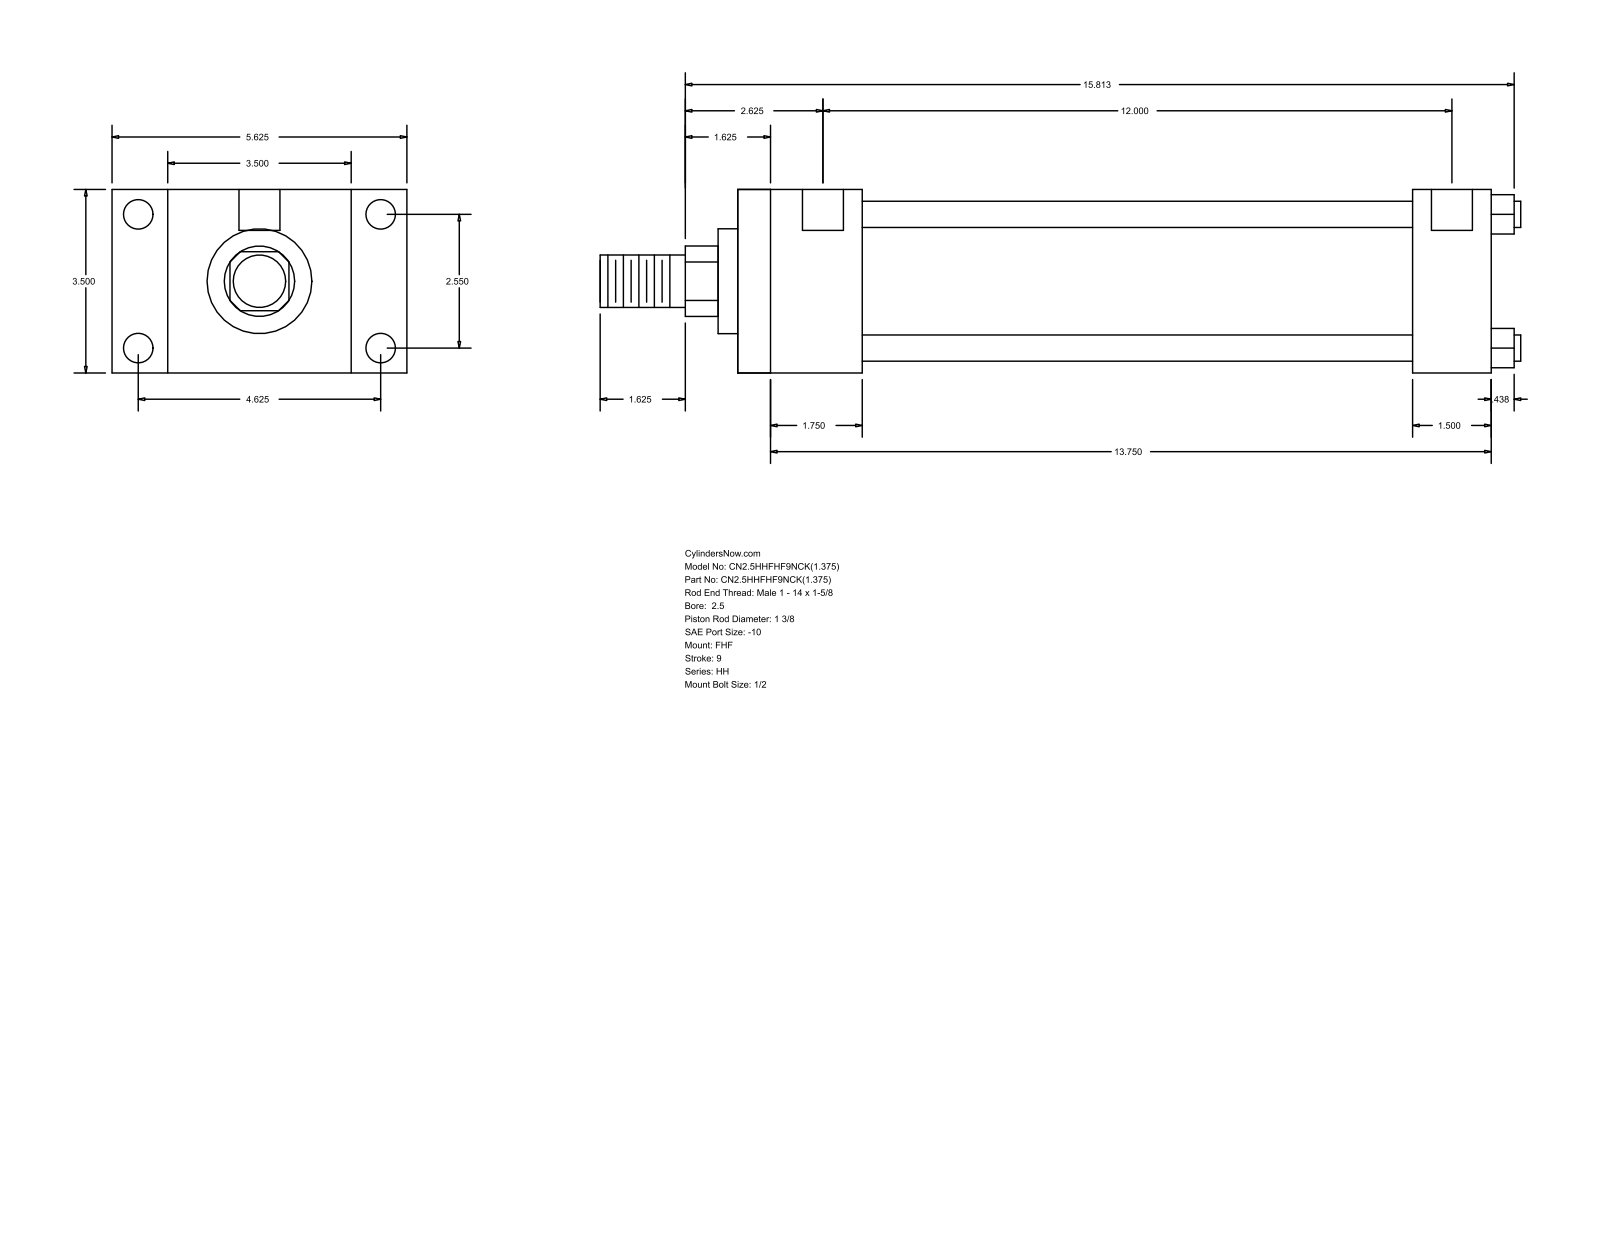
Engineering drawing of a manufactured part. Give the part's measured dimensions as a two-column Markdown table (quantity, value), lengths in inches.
| quantity | value |
| --- | --- |
| part name | HH_FHF__0250_1.375 |
| STEP written by | GSSL Pune (CONFIG_CONTROL_DESIGN) |
| units | inches |
| bodies | 0 solids, 88 faces (60 planar, 28 cylindrical, 0 other) |
| overall size | 17.563 × 5.625 × 3.5 |
| round holes (diameter × count) | 0.219 × 4, 0.563 × 4, 0.781 × 2 |
| round bosses / shafts (diameter × count) | 0.5 × 4, 2.875 × 1, 2 × 1, 1.375 × 1, 1 × 1 |
| partial cylindrical surfaces (radius × count) | 0.672 × 1 |
| main face-to-face distances | 3.5, 2.375, 1.063, 4.563, 14.375, 12, 5.625, 12.875, 10.5, 1.5 |
| hole center spacings | 0.062, 2.55, 4.625, 5.281, 12.063, 12.125, 12 |
